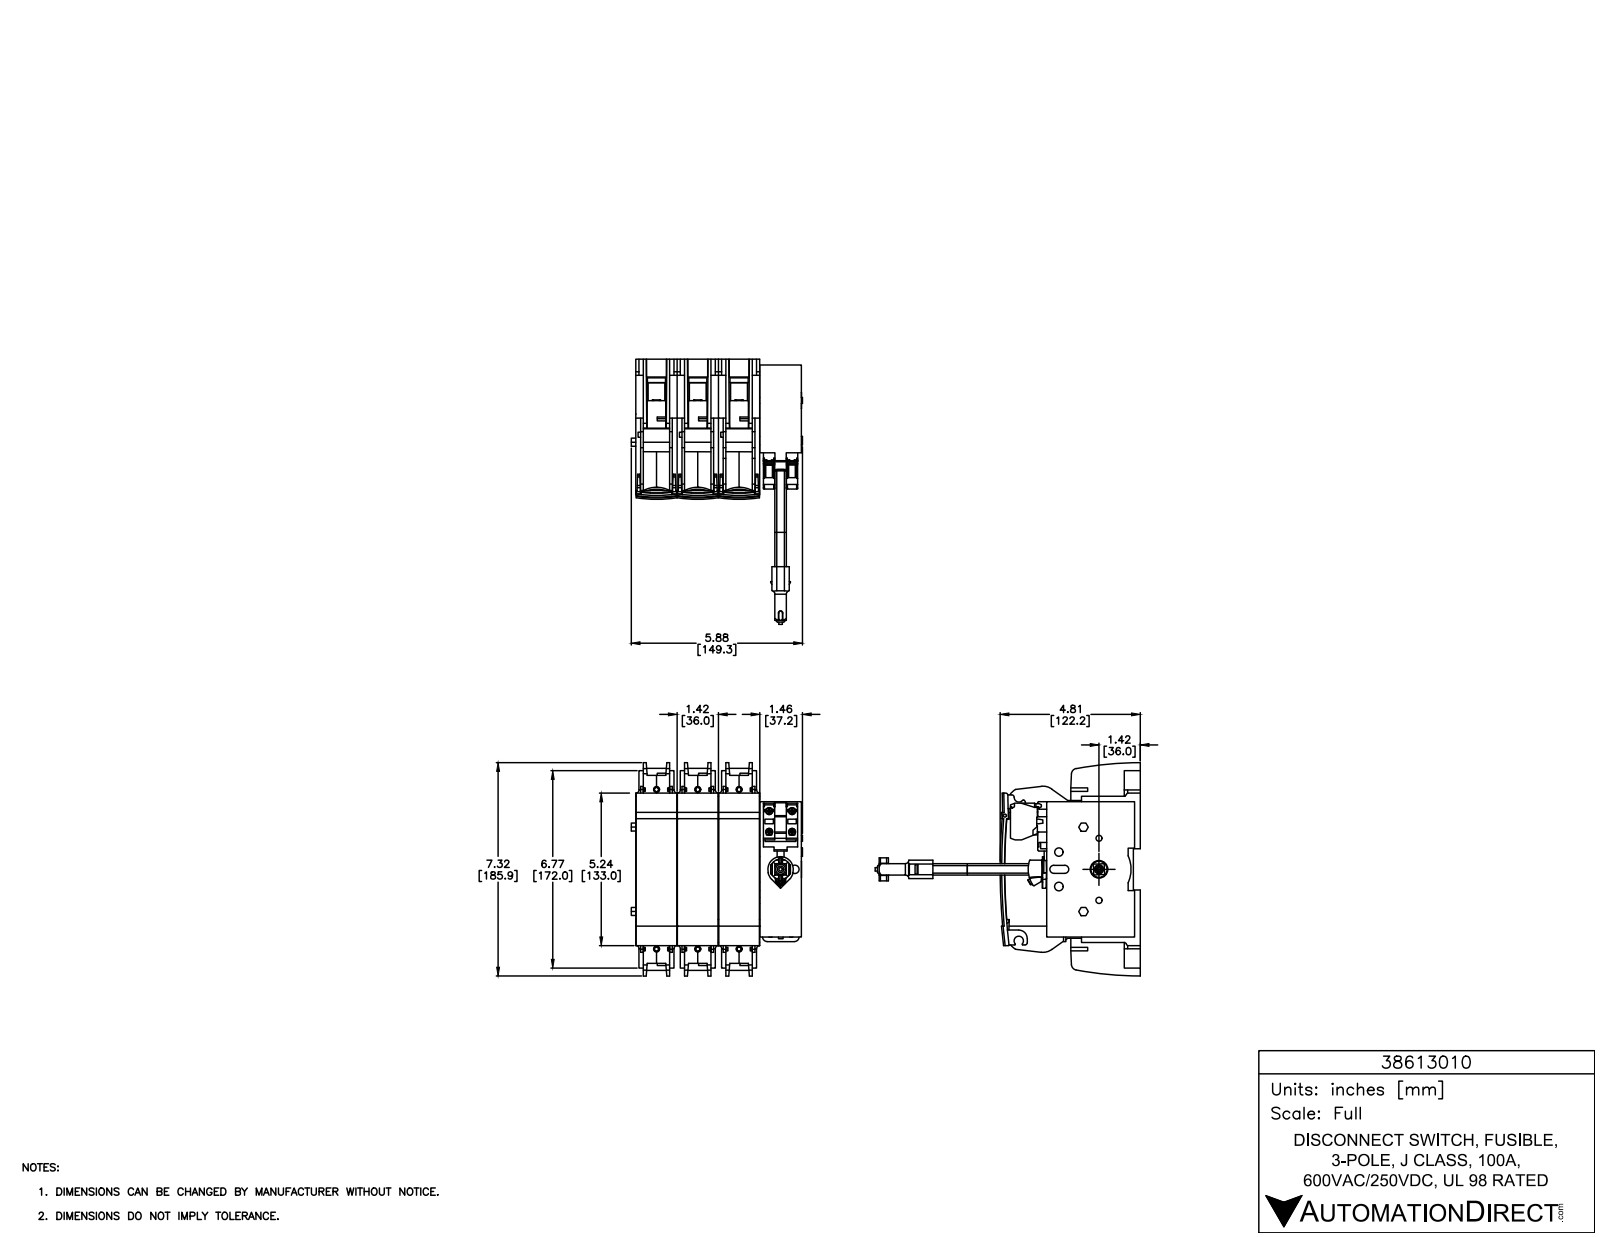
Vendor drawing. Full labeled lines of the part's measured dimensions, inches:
Part name (STEP PRODUCT): 38613010
STEP written by: SolidWorks 2015 (AUTOMOTIVE_DESIGN)
Units: inches
Bodies: 7 solids, 1776 faces (1009 planar, 310 cylindrical, 457 other)
Overall size (bounding box): 7.323 × 5.72 × 4.813
Volume: 125.3 in³ · Surface area: 427.8 in²
Round holes (diameter × count): ⌀0.205 ×6, ⌀0.209 ×2, ⌀0.211 ×2, ⌀0.295 ×2, ⌀0.098 ×1, ⌀0.102 ×1, ⌀0.13 ×1, ⌀0.283 ×1, ⌀0.602 ×1, ⌀0.622 ×1
Round bosses / shafts (diameter × count): ⌀0.287 ×2, ⌀0.205 ×2, ⌀0.203 ×2, ⌀0.63 ×1, ⌀0.315 ×1, ⌀0.197 ×1
Partial cylindrical surfaces — rounded edges, fillets, slot ends (radius × count): R0.106 ×24, R0.248 ×12, R0.346 ×12, R0.02 ×7, R0.043 ×6, R0.201 ×6, R0.039 ×5, R0.138 ×3
Main face-to-face distances: 1.417, 2.835, 0.256, 1.161, 0.165, 1.252, 0.091, 0.996, 2.579, 1.673
Hole centre spacings: 1.417, 5.653, 5.472, 1.067, 1.458, 1.499, 2.156, 2.835
